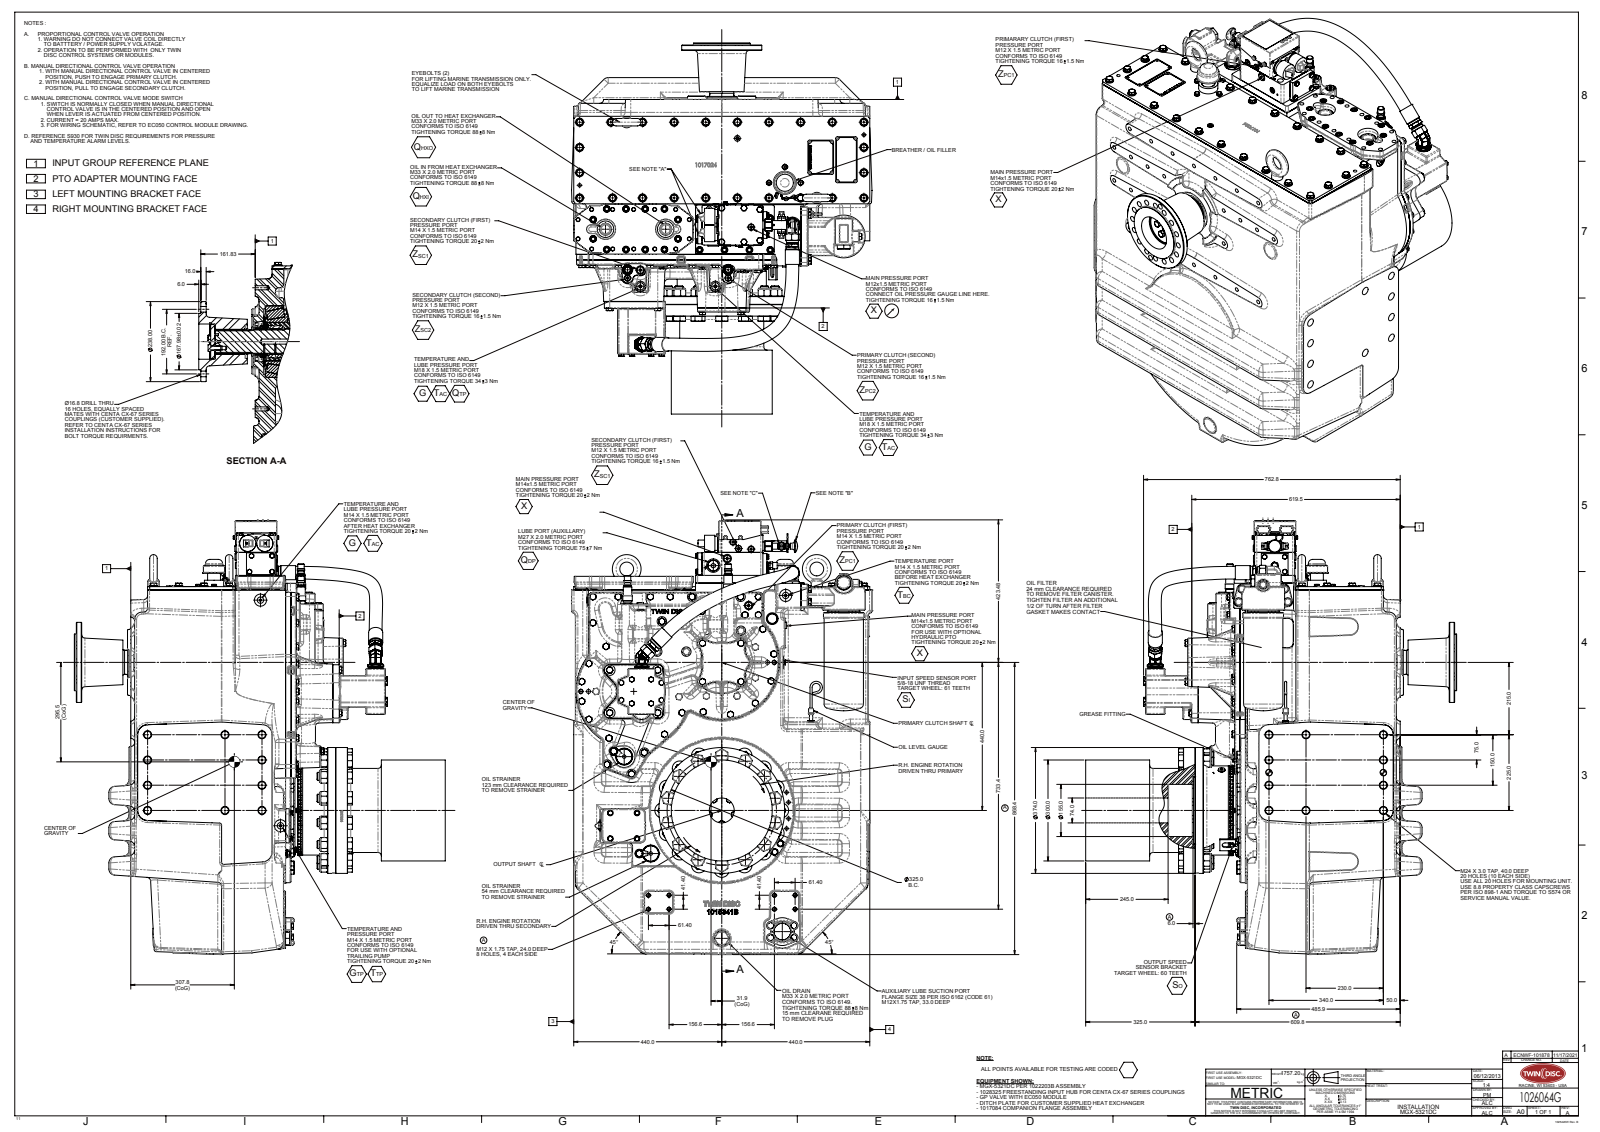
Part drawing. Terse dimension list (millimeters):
name: 1026064G
written by: SolidWorks 2015 (CONFIG_CONTROL_DESIGN)
unit: mm
bodies: 0 solids, 5442 faces (1912 planar, 1621 cylindrical, 1909 other)
size: 1291.85 × 1103 × 893
holes: 51× ⌀12, 17× ⌀20, 16× ⌀16.8, 10× ⌀24, 8× ⌀10, 5× ⌀16, 4× ⌀10.2, 4× ⌀44.5, 3× ⌀25, 3× ⌀28, 2× ⌀17.45, 2× ⌀19.06
bosses: 29× ⌀24, 18× ⌀18, 14× ⌀35.5, 8× ⌀19, 7× ⌀17, 3× ⌀13, 3× ⌀2.54, 3× ⌀1.52
rounds: 129× R12, 108× R3, 90× R43.44, 79× R6, 45× R2.54, 43× R18, 39× R0.5, 28× R3.05
face distances: 0.5, 16.5, 16, 448.5, 10.09, 465, 17, 465.5, 15.5, 22.5
hole spacings: 57.15, 70, 90, 138.92, 75, 133.5, 140, 348.17
